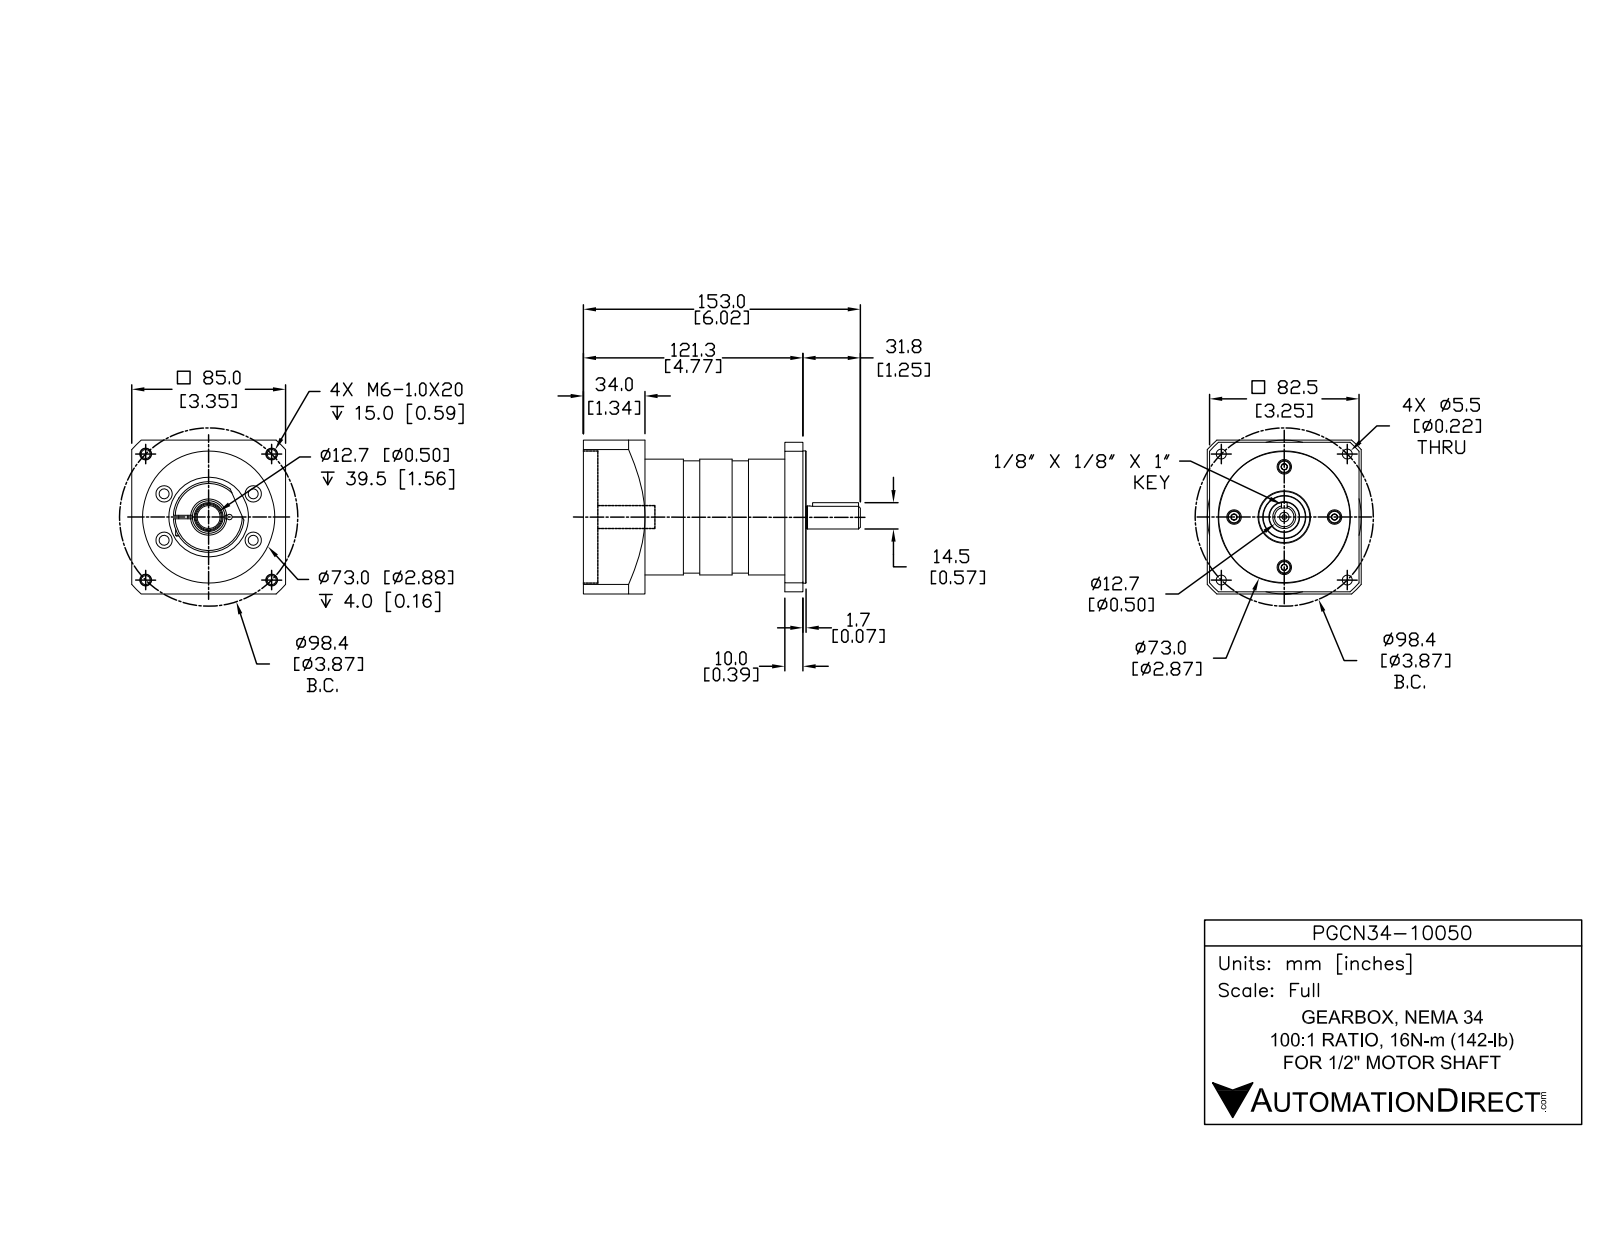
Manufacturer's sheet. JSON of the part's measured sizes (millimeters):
{"part_name": "PGCN34-10050; Bushing_.5x14x20.5; N34-A06; PE-N34-II 14mm Input", "step_written_by": "SolidWorks 2014 (AUTOMOTIVE_DESIGN)", "units": "millimeters", "bodies": {"solids": 3, "faces": 368, "planar": 108, "cylindrical": 146, "other": 114}, "overall_size": [153.1, 85, 85], "volume_mm3": 501400, "surface_area_mm2": 75610, "round_holes": [[5, 5], [9, 5], [3.3, 4], [4, 4], [5.5, 4], [5.5, 4], [6, 4], [8, 4], [14, 2], [2.5, 1], [12.7, 1], [28.2, 1]], "round_bosses_or_shafts": [[7, 4], [73, 1], [64, 1], [62, 1], [39, 1], [23.8, 1], [23.3, 1], [20, 1]], "partial_cylinders_radius": [[1.5, 1], [1.6, 1], [9, 1], [55, 1], [56.5, 1]], "face_to_face_distances": [85, 11.8, 123, 111.3, 10, 34, 87.3, 33, 78.3, 1.8], "hole_center_spacings": [35.5, 71.6, 13.2, 24.2, 27.7, 27.8, 28.8, 39.2]}
